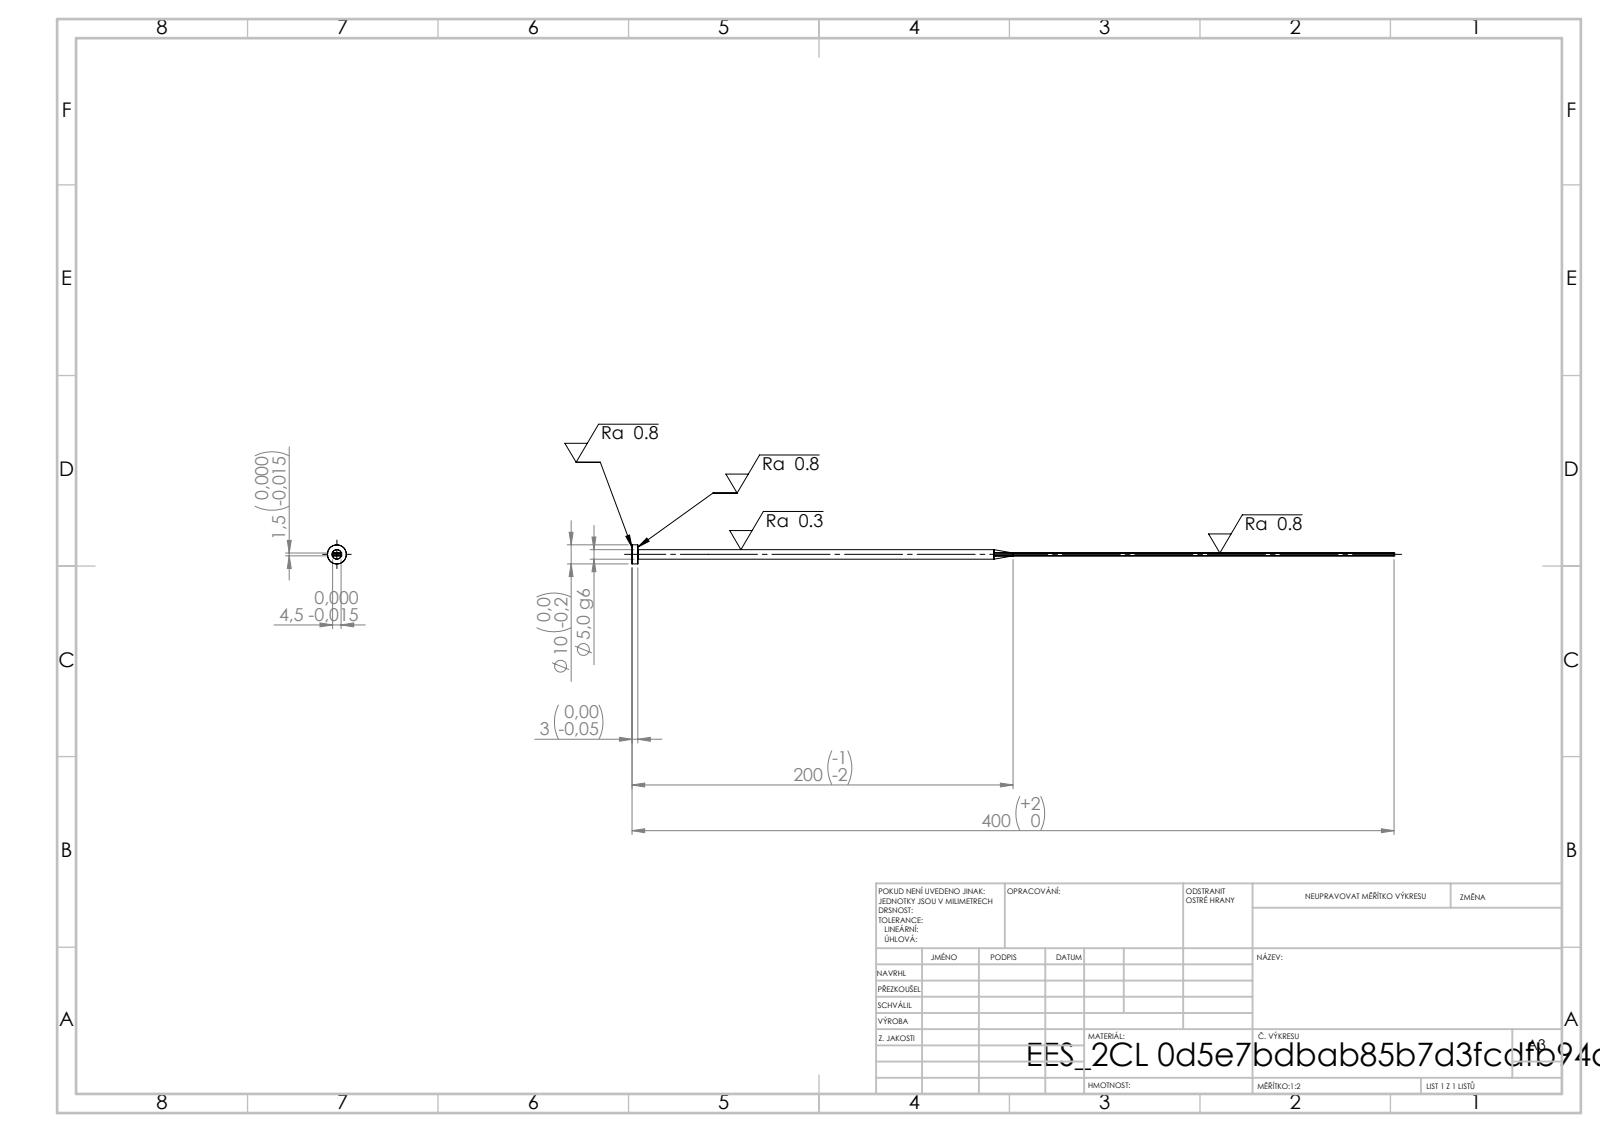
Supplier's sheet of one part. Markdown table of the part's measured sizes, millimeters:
| quantity | value |
| --- | --- |
| STEP written by | SolidWorks 2019 (CONFIG_CONTROL_DESIGN) |
| units | millimeters |
| bodies | 1 solid, 15 faces (7 planar, 4 cylindrical, 4 other) |
| overall size | 400 × 10 × 10 |
| volume | 5 385 mm³ |
| surface area | 5 710 mm² |
| round bosses / shafts (diameter × count) | 10 × 1, 5 × 1 |
| main face-to-face distances | 1.5, 4.5, 3, 400, 397 |
